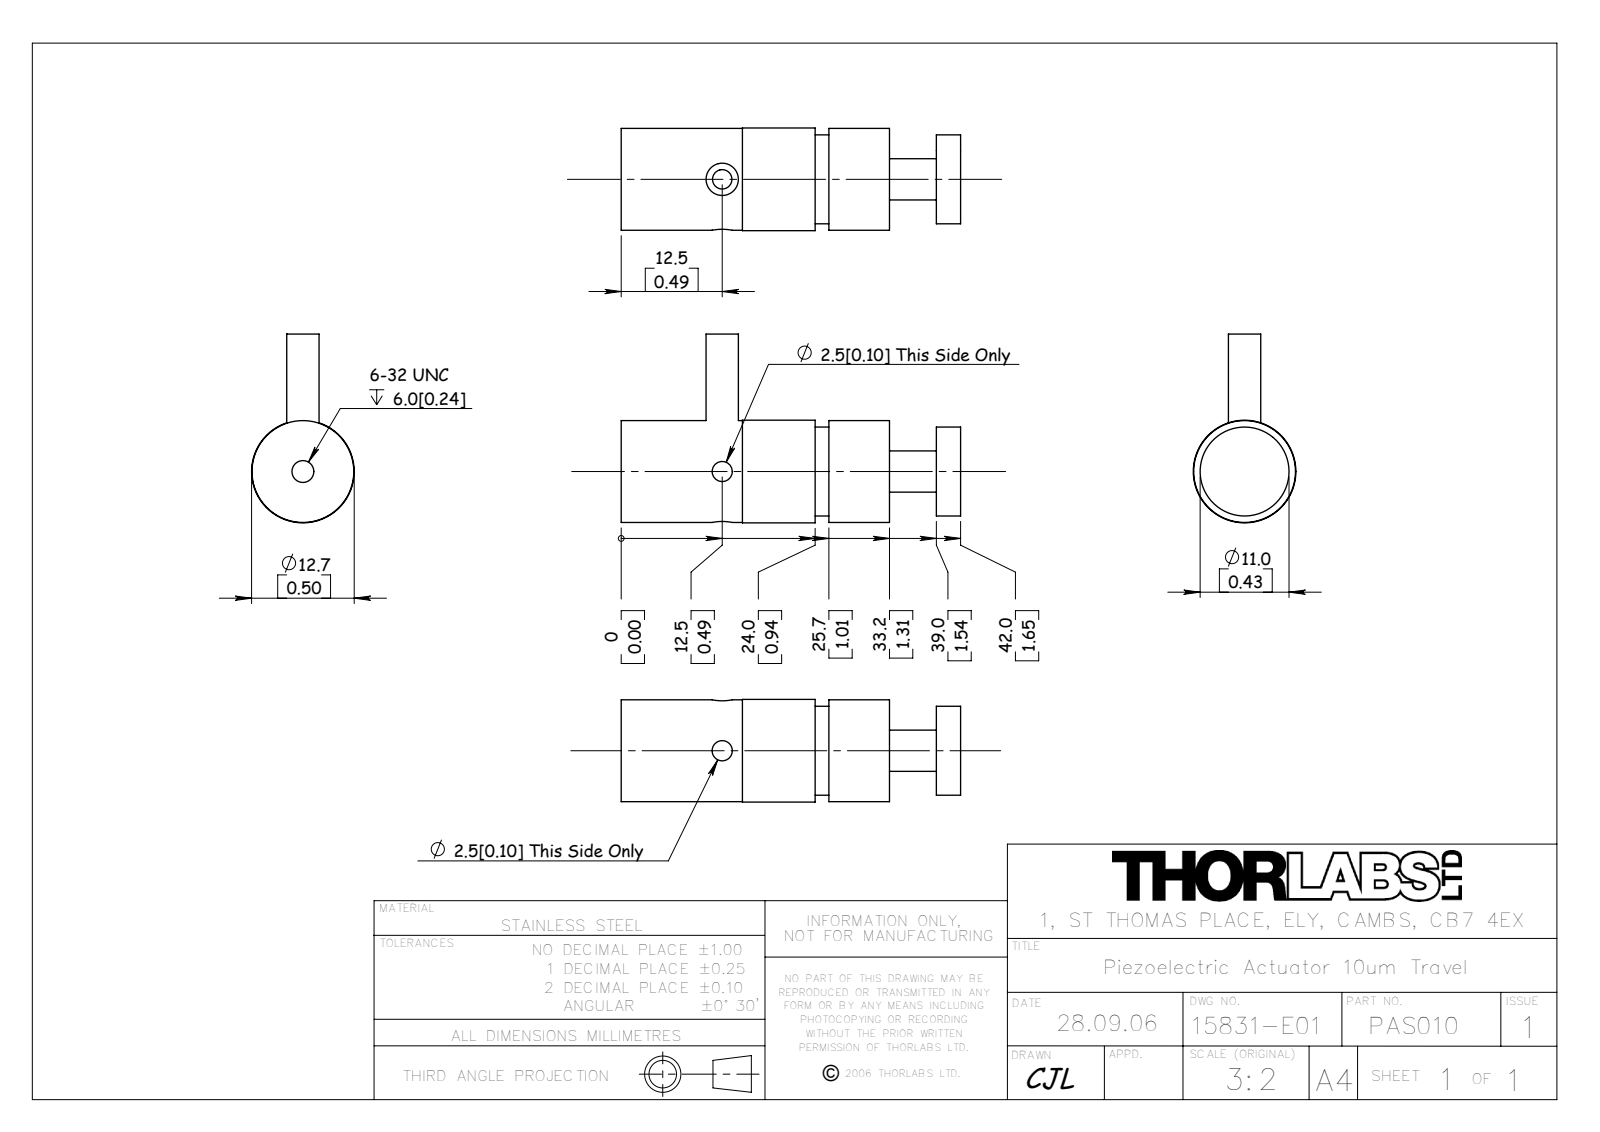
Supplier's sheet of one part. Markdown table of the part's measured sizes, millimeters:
| quantity | value |
| --- | --- |
| part name | 15831-E0W |
| STEP written by | SolidWorks 2007 (CONFIG_CONTROL_DESIGN) |
| units | millimeters |
| bodies | 0 solids, 38 faces (10 planar, 28 cylindrical, 0 other) |
| overall size | 42 × 23.35 × 12.7 |
| round holes (diameter × count) | 2.5 × 2, 2.4 × 1, 2.71 × 1, 5.3 × 1, 9.55 × 1, 11.4 × 1 |
| round bosses / shafts (diameter × count) | 12.7 × 1, 12.6 × 1, 11 × 1, 5.1 × 1, 4 × 1 |
| main face-to-face distances | 33.2, 8.8, 42, 3, 5.8, 39, 32, 29, 23.2, 10 |
